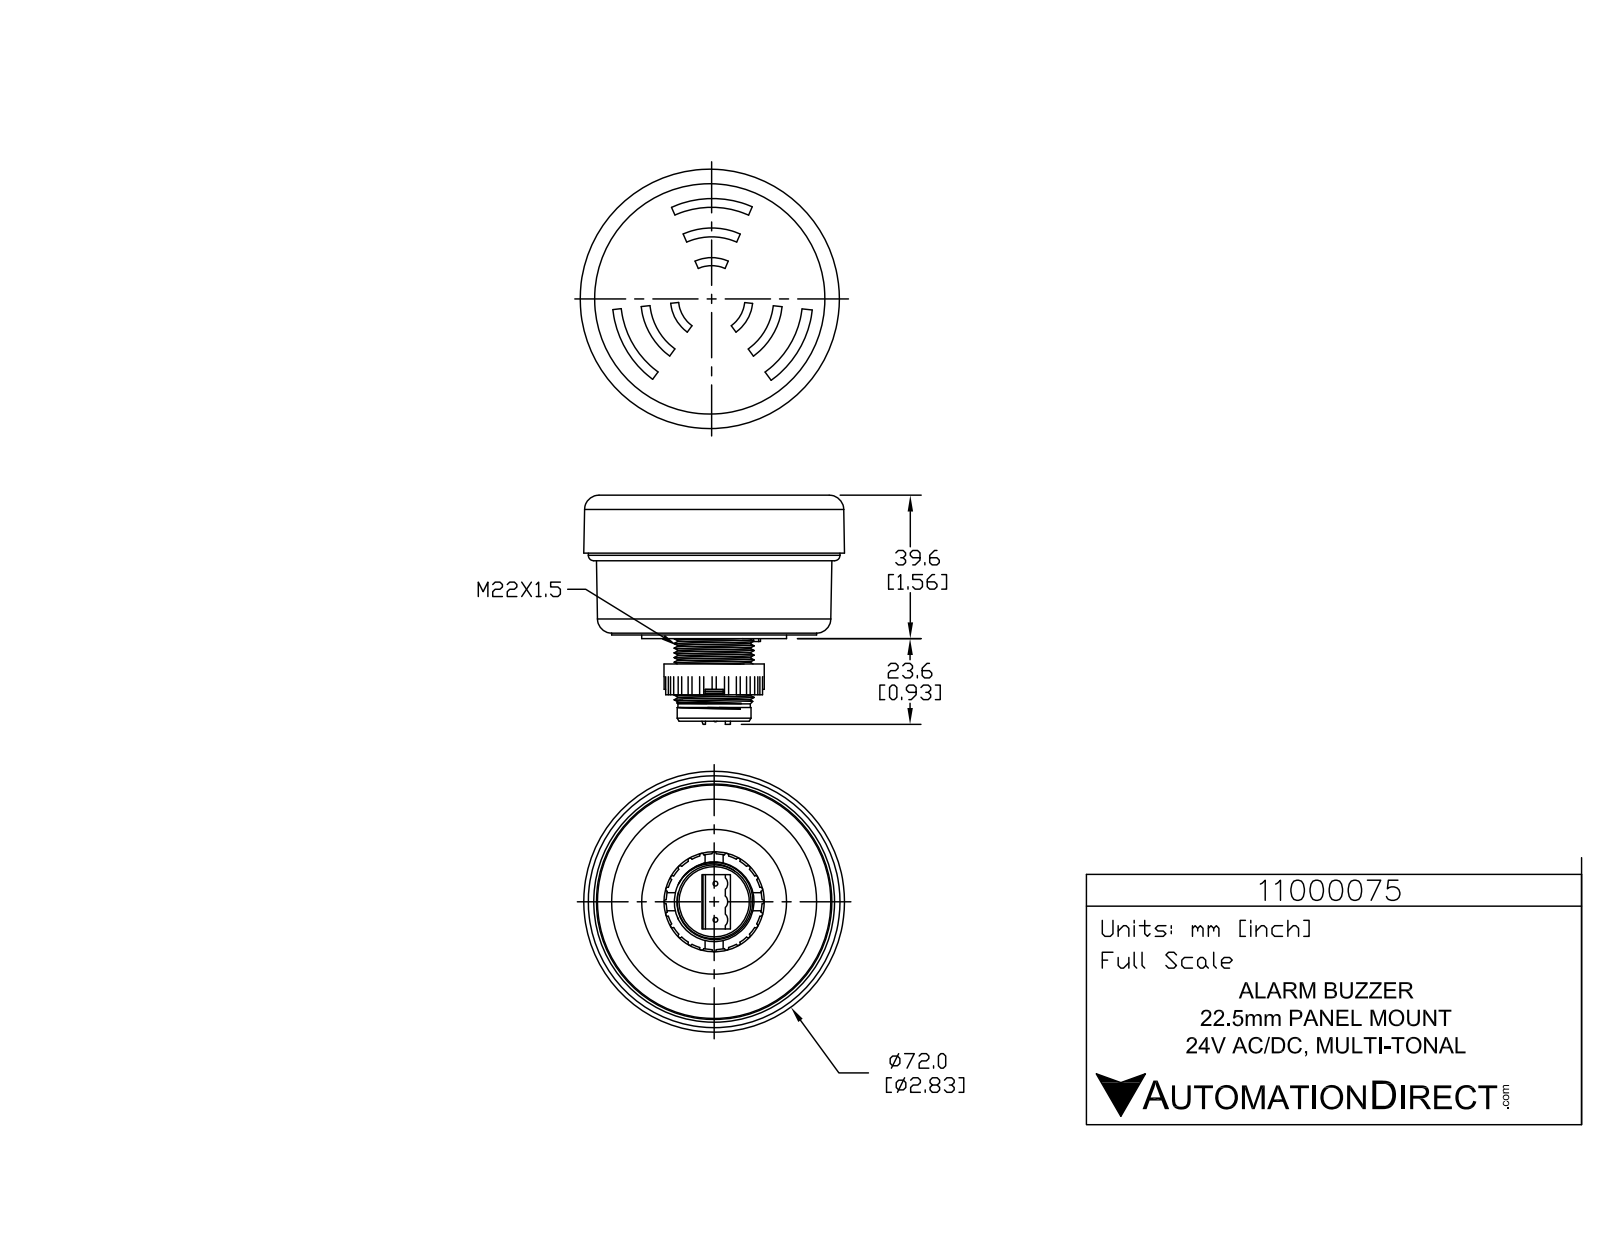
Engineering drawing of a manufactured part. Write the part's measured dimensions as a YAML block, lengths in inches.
part_name: "11000075"
step_written_by: "SolidWorks 2017 (AUTOMOTIVE_DESIGN)"
units: inches
bodies: {solids: 1, faces: 1199, planar: 768, cylindrical: 326, other: 105}
overall_size: [2.839, 2.837, 2.49]
volume: 9.029
surface_area: 31.77
round_holes:
  - {diameter: 0.049, count: 3}
  - {diameter: 0.106, count: 1}
  - {diameter: 0.424, count: 1}
  - {diameter: 0.906, count: 1}
round_bosses_or_shafts:
  - {diameter: 0.282, count: 3}
  - {diameter: 0.07, count: 3}
  - {diameter: 0.051, count: 2}
  - {diameter: 2.736, count: 1}
  - {diameter: 2.228, count: 1}
  - {diameter: 1.575, count: 1}
  - {diameter: 1.091, count: 1}
  - {diameter: 0.866, count: 1}
partial_cylinders:
  - {radius: 0.023, count: 24}
  - {radius: 0.004, count: 9}
  - {radius: 0.004, count: 6}
  - {radius: 0.01, count: 6}
  - {radius: 0.01, count: 6}
  - {radius: 0.01, count: 6}
  - {radius: 0.164, count: 6}
  - {radius: 0.004, count: 3}
face_to_face_distances: [1.52, 0.039, 1.559, 0.63, 0.89, 0.929, 0.276, 0.626, 1.555, 1.516]
hole_center_spacings: [0.407, 0.613, 0.973]
